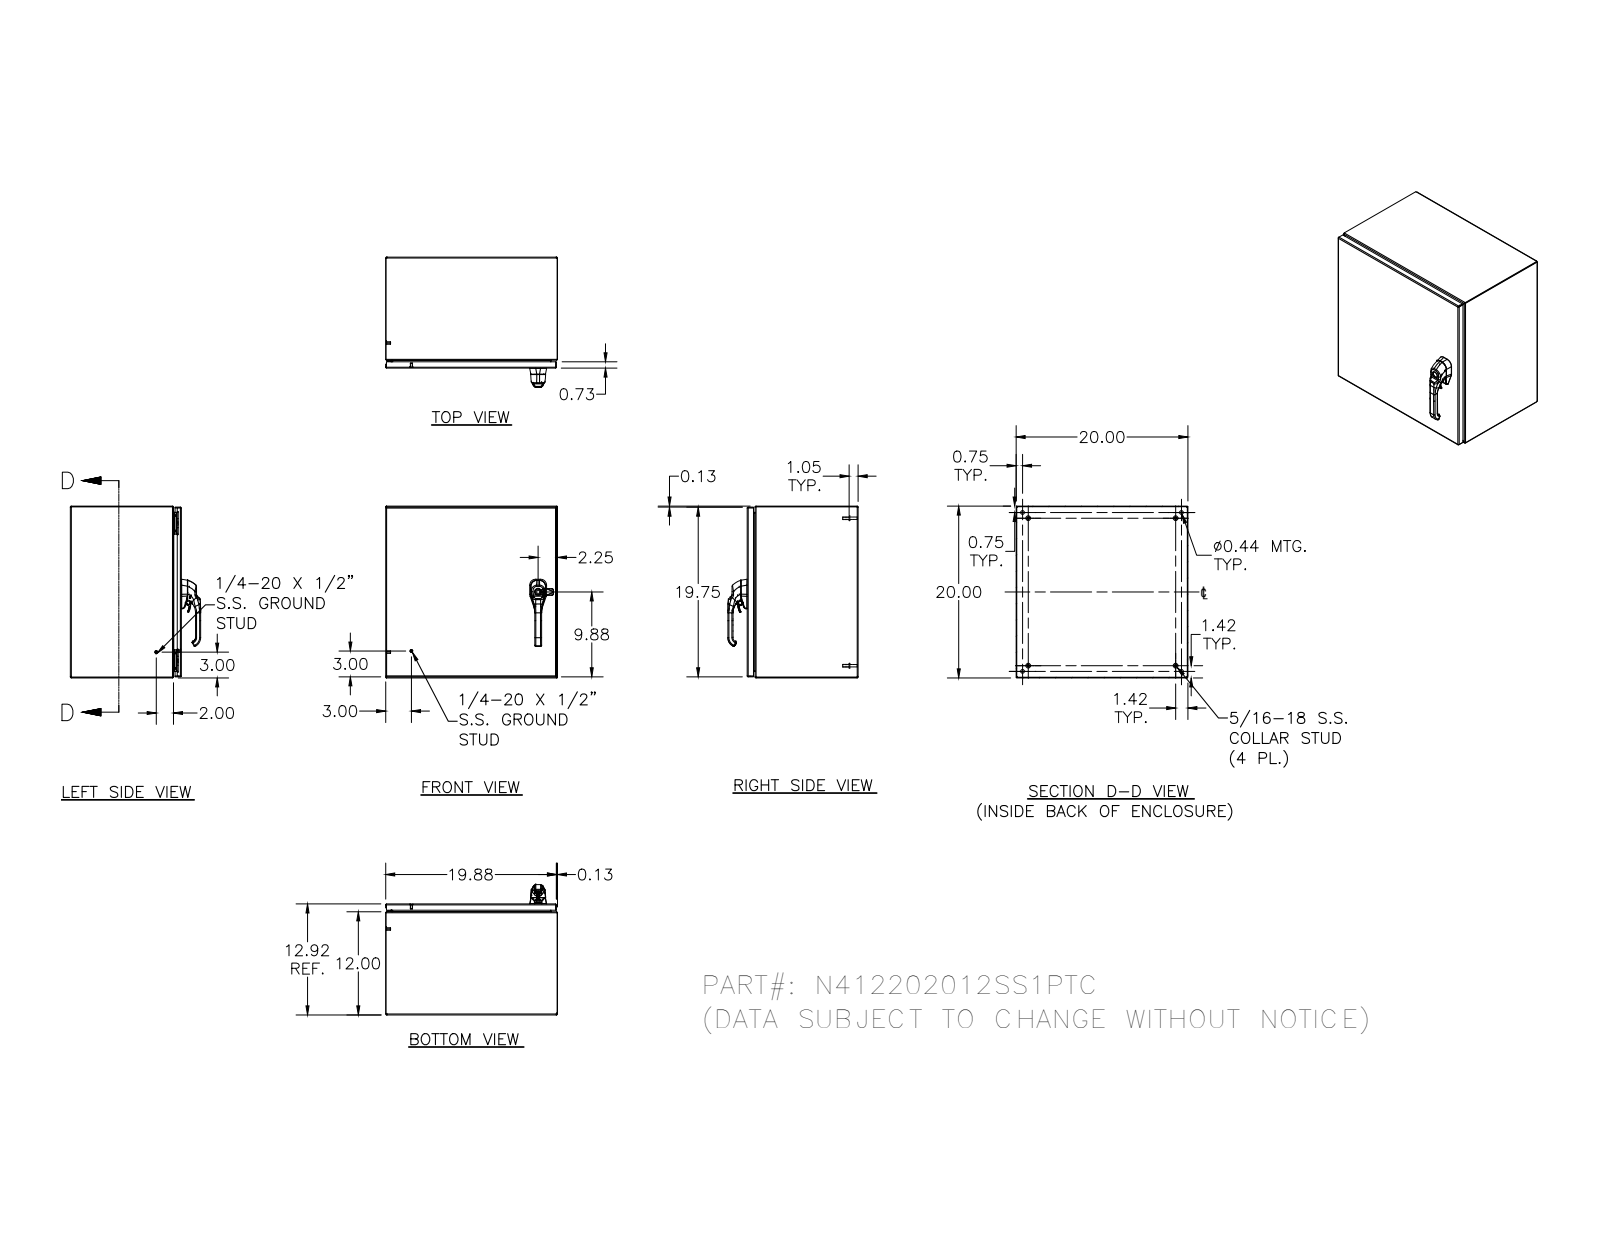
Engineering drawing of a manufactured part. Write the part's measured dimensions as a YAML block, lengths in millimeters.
part_name: "N412202012SS1PTC; N412202012SS1PTCBKP; N4122020SS1PTCLID; HFW328176 (+8 more)"
step_written_by: "Autodesk Inventor 2012 (AUTOMOTIVE_DESIGN)"
units: millimeters
bodies: {solids: 41, faces: 2782, planar: 882, cylindrical: 1035, other: 865}
overall_size: [508, 508, 385.2]
volume: 2443000
surface_area: 2550000
round_holes:
  - {diameter: 2.4, count: 4}
  - {diameter: 3.9, count: 4}
  - {diameter: 4.2, count: 4}
  - {diameter: 4.4, count: 4}
  - {diameter: 4.8, count: 4}
  - {diameter: 11.1, count: 4}
  - {diameter: 5.4, count: 3}
  - {diameter: 7.1, count: 3}
  - {diameter: 4, count: 2}
  - {diameter: 8, count: 2}
  - {diameter: 10.2, count: 2}
  - {diameter: 10.5, count: 2}
round_bosses_or_shafts:
  - {diameter: 6.4, count: 10}
  - {diameter: 14.3, count: 4}
  - {diameter: 9.1, count: 4}
  - {diameter: 8.1, count: 4}
  - {diameter: 7.6, count: 4}
  - {diameter: 7, count: 4}
  - {diameter: 6.5, count: 4}
  - {diameter: 4.2, count: 4}
partial_cylinders:
  - {radius: 0.5, count: 174}
  - {radius: 0.3, count: 101}
  - {radius: 0.8, count: 30}
  - {radius: 1.3, count: 26}
  - {radius: 0.5, count: 21}
  - {radius: 2.7, count: 20}
  - {radius: 0.4, count: 18}
  - {radius: 2, count: 14}
face_to_face_distances: [1.9, 506.1, 326.2, 504.2, 508, 328.1, 324.3, 302.9, 23.3, 18.8]
hole_center_spacings: [406.3, 469.9, 479.3, 0.4, 16.8, 406.5, 423.1, 0.5]
